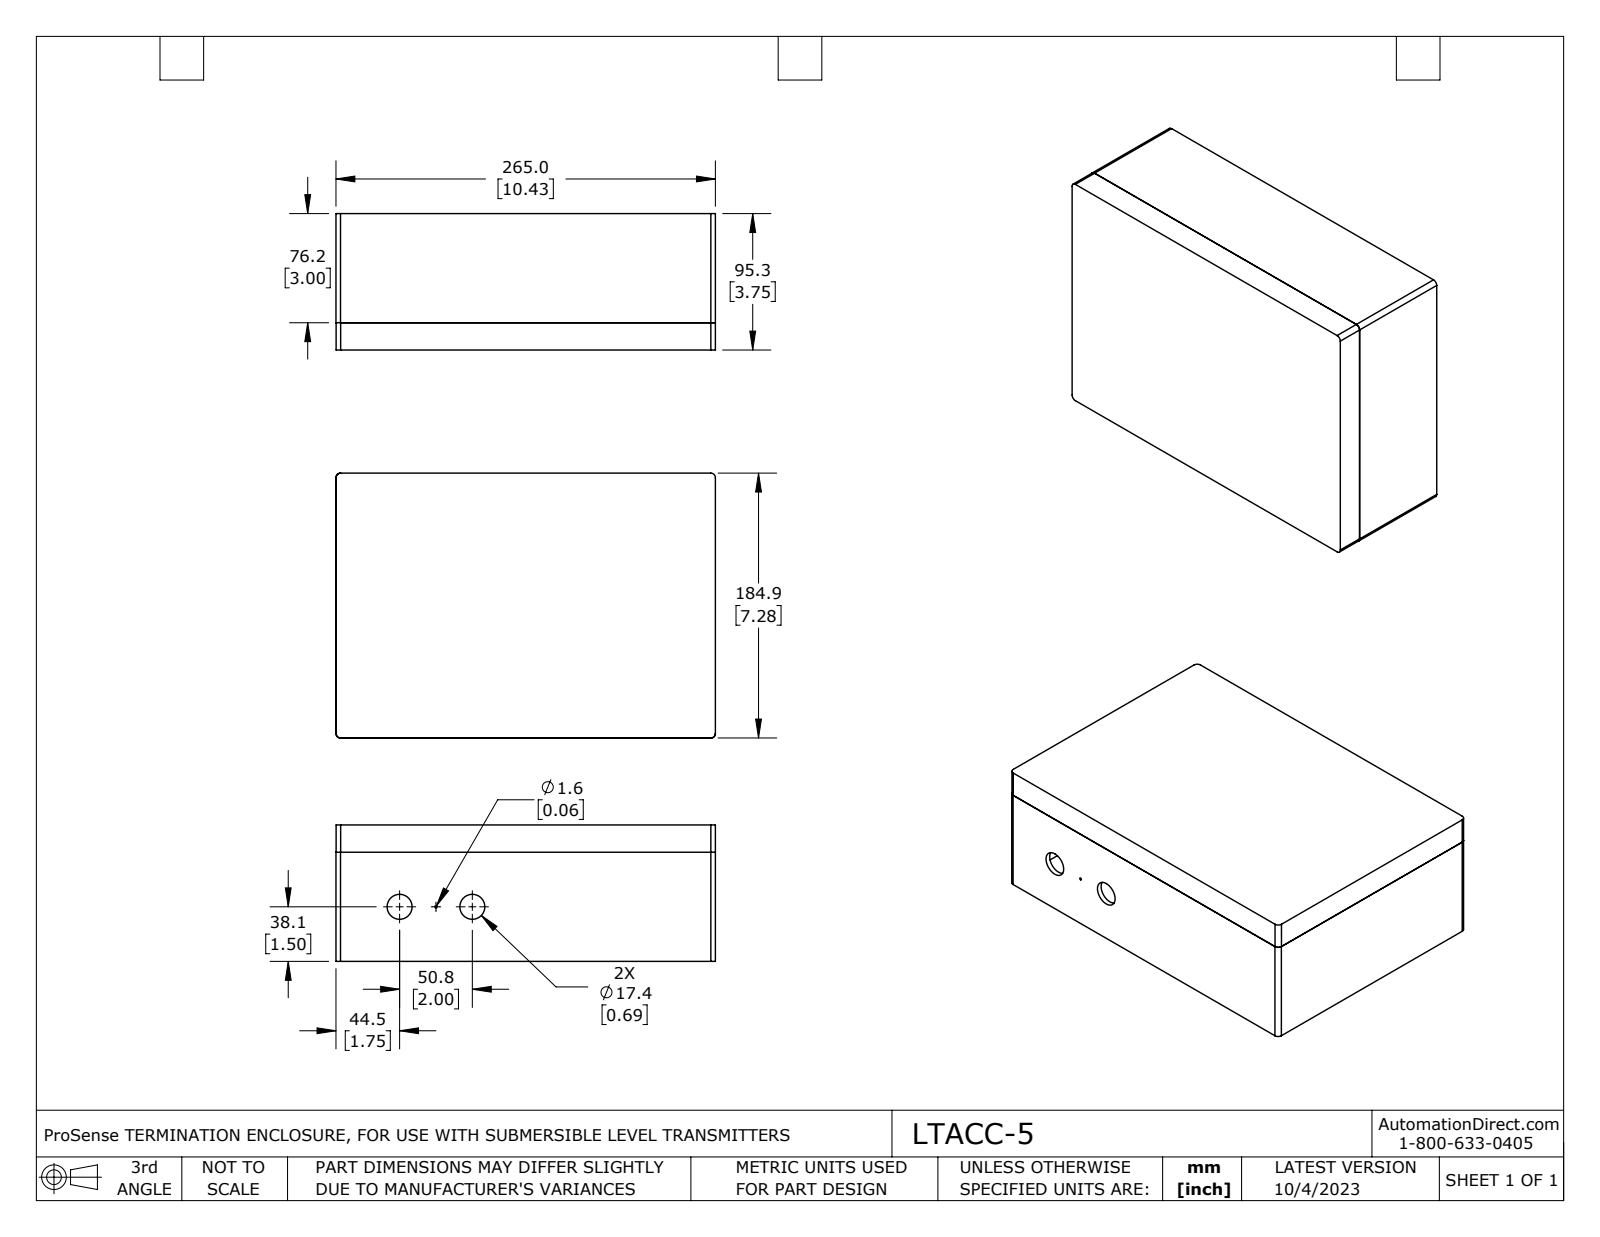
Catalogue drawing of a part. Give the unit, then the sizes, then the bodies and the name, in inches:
Units: inches
Overall size (bounding box): 10.434 × 7.284 × 3.75
Round holes (diameter × count): ⌀0.687 ×2, ⌀0.062 ×1
Partial cylindrical surfaces — rounded edges, fillets, slot ends (radius × count): R0.125 ×11
Main face-to-face distances: 3.75, 3.7, 0.05, 0.2, 3.5, 3.55, 0.142, 7.142, 0.217, 10.217
Hole centre spacings: 1, 2
Volume: 38.74 in³ · Surface area: 553.7 in²
Bodies: 2 solids, 42 faces (22 planar, 18 cylindrical, 2 other)
Part name (STEP PRODUCT): LTACC-5
STEP written by: SolidWorks 2021 (AUTOMOTIVE_DESIGN)
